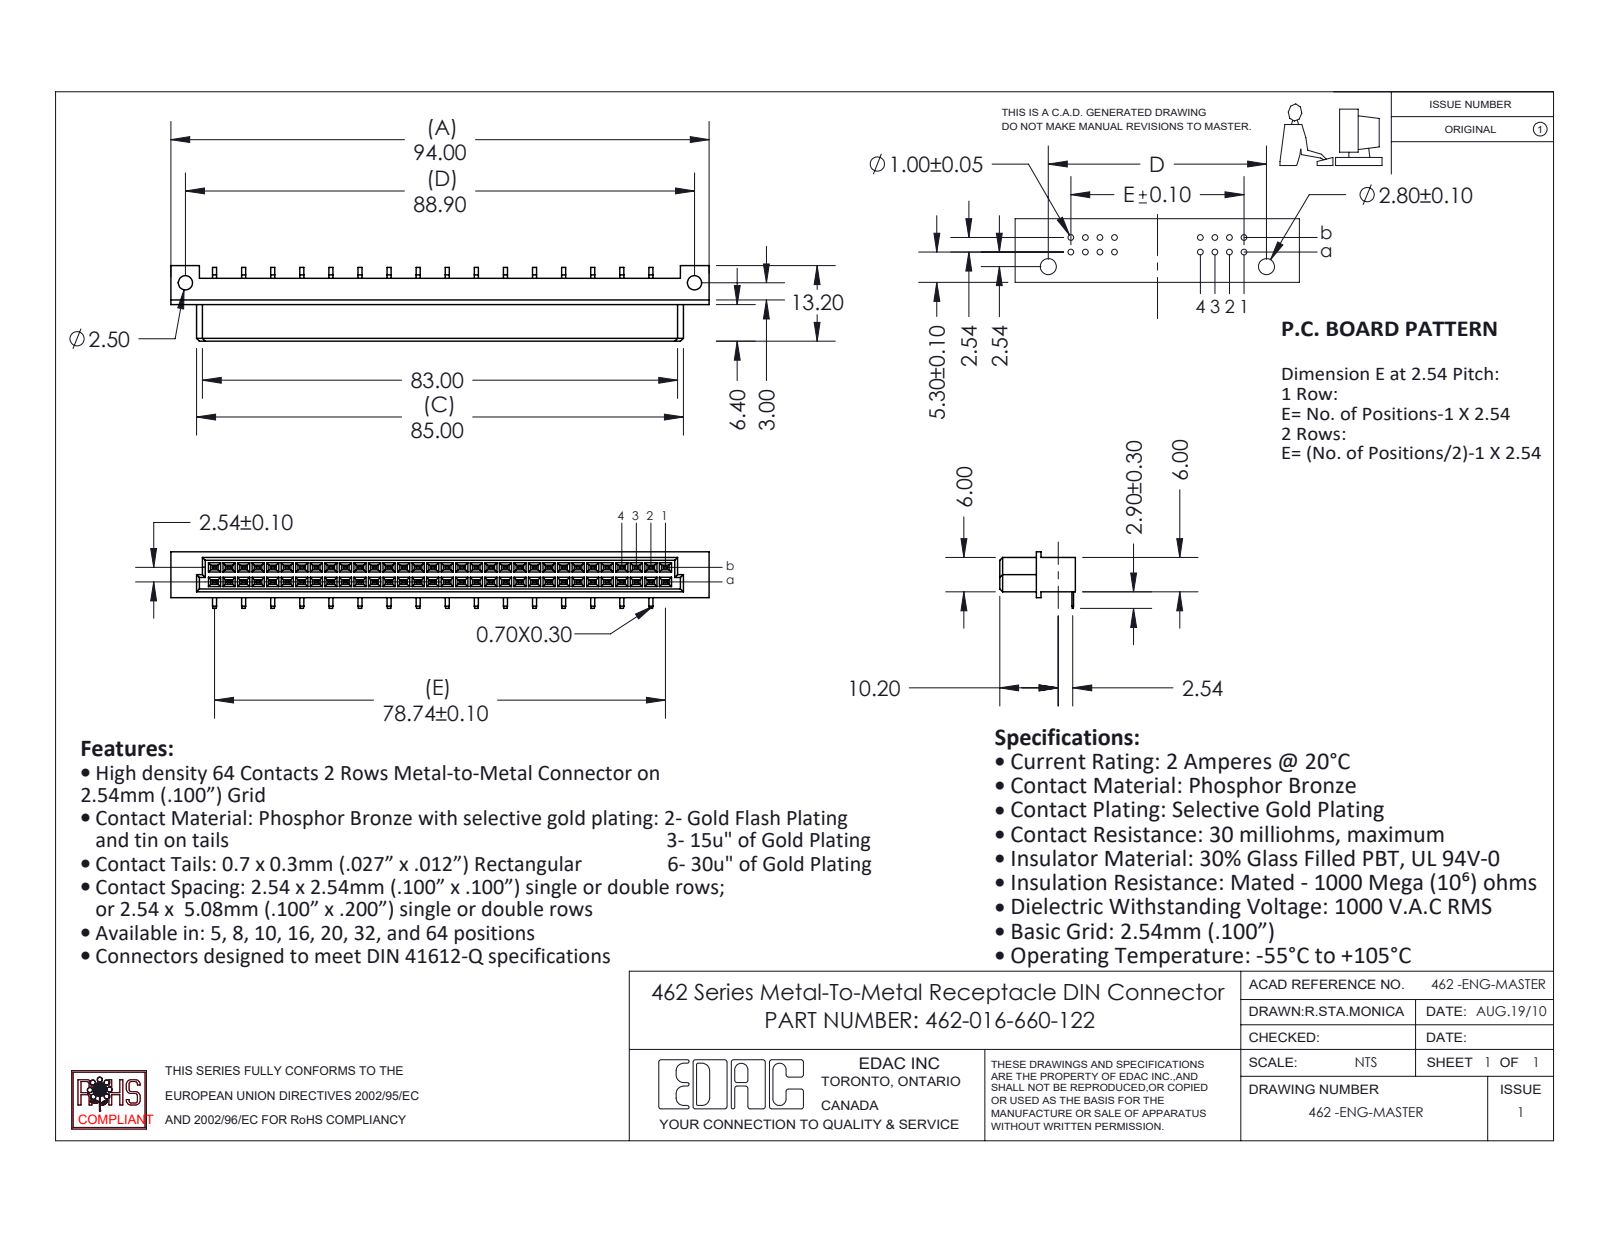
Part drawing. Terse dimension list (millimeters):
name: 462-016-660-122; 462-290-1; 462 Part_64
written by: SolidWorks 2020 (CONFIG_CONTROL_DESIGN)
unit: mm
bodies: 17 solids, 1091 faces (1055 planar, 36 cylindrical, 0 other)
size: 94 × 13.2 × 9.9
volume: 5 527 mm³; area: 6 252 mm²
holes: 2× ⌀2.5
rounds: 1× R1.02, 1× R1.32
face distances: 6, 2.54, 0.81, 4.6, 1.32, 2.13, 3.86, 4.67, 3.35, 4.68
hole spacings: 88.9
